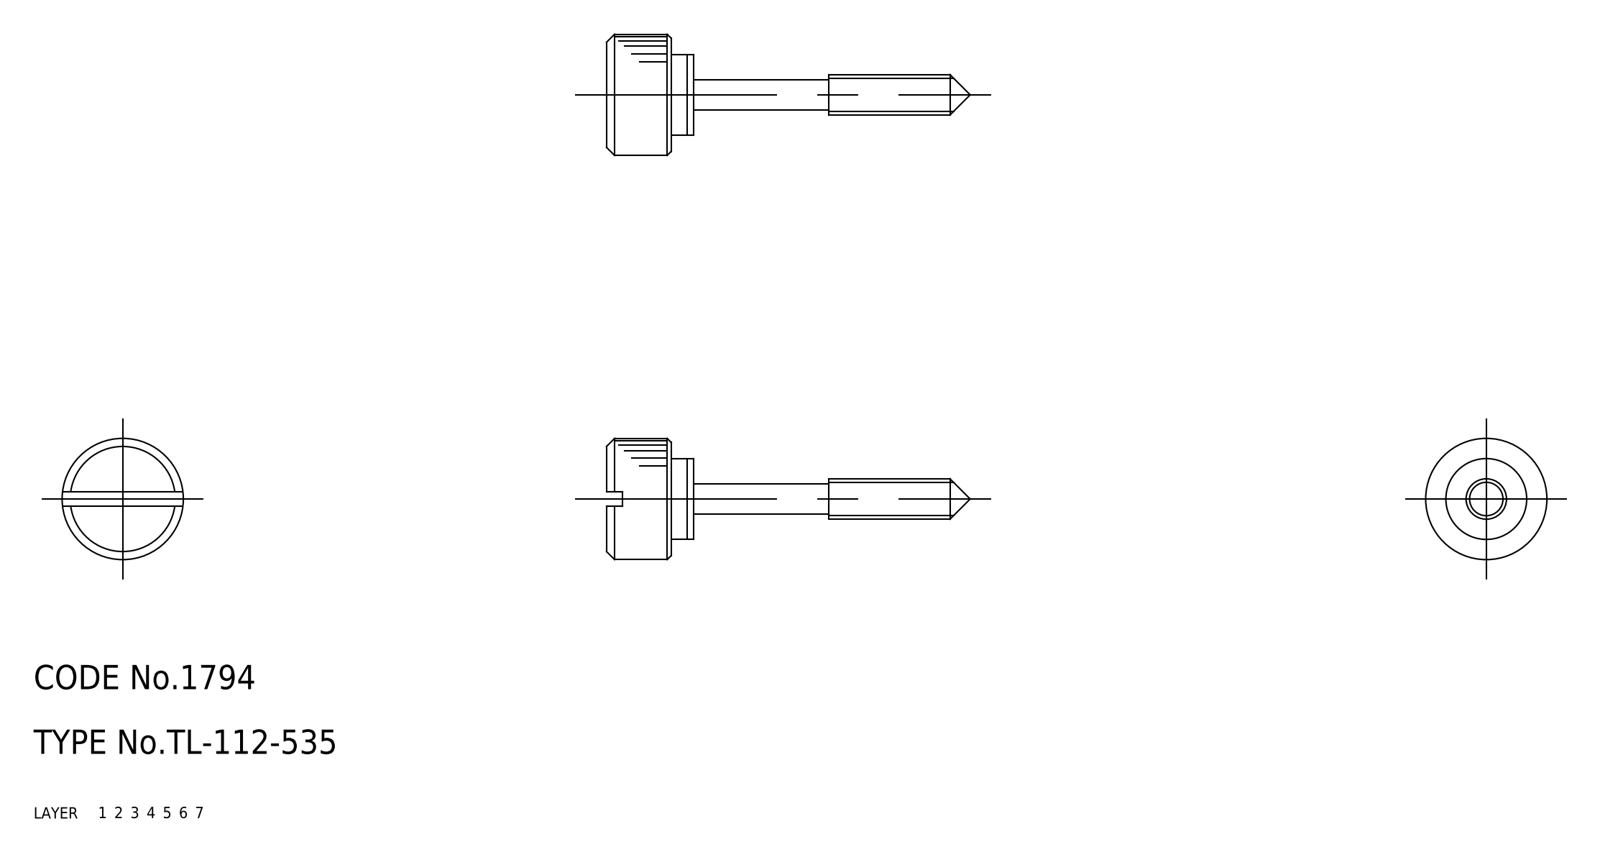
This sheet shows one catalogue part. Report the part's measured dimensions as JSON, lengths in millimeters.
{"part_name": "washer; knob; TL_112_535_8779_36", "step_written_by": "CADfix (AUTOMOTIVE_DESIGN)", "units": "millimeters", "bodies": {"solids": 2, "faces": 42, "planar": 0, "cylindrical": 0, "other": 42}, "overall_size": [45, 15, 15], "volume_mm3": 2052, "surface_area_mm2": 1434}
